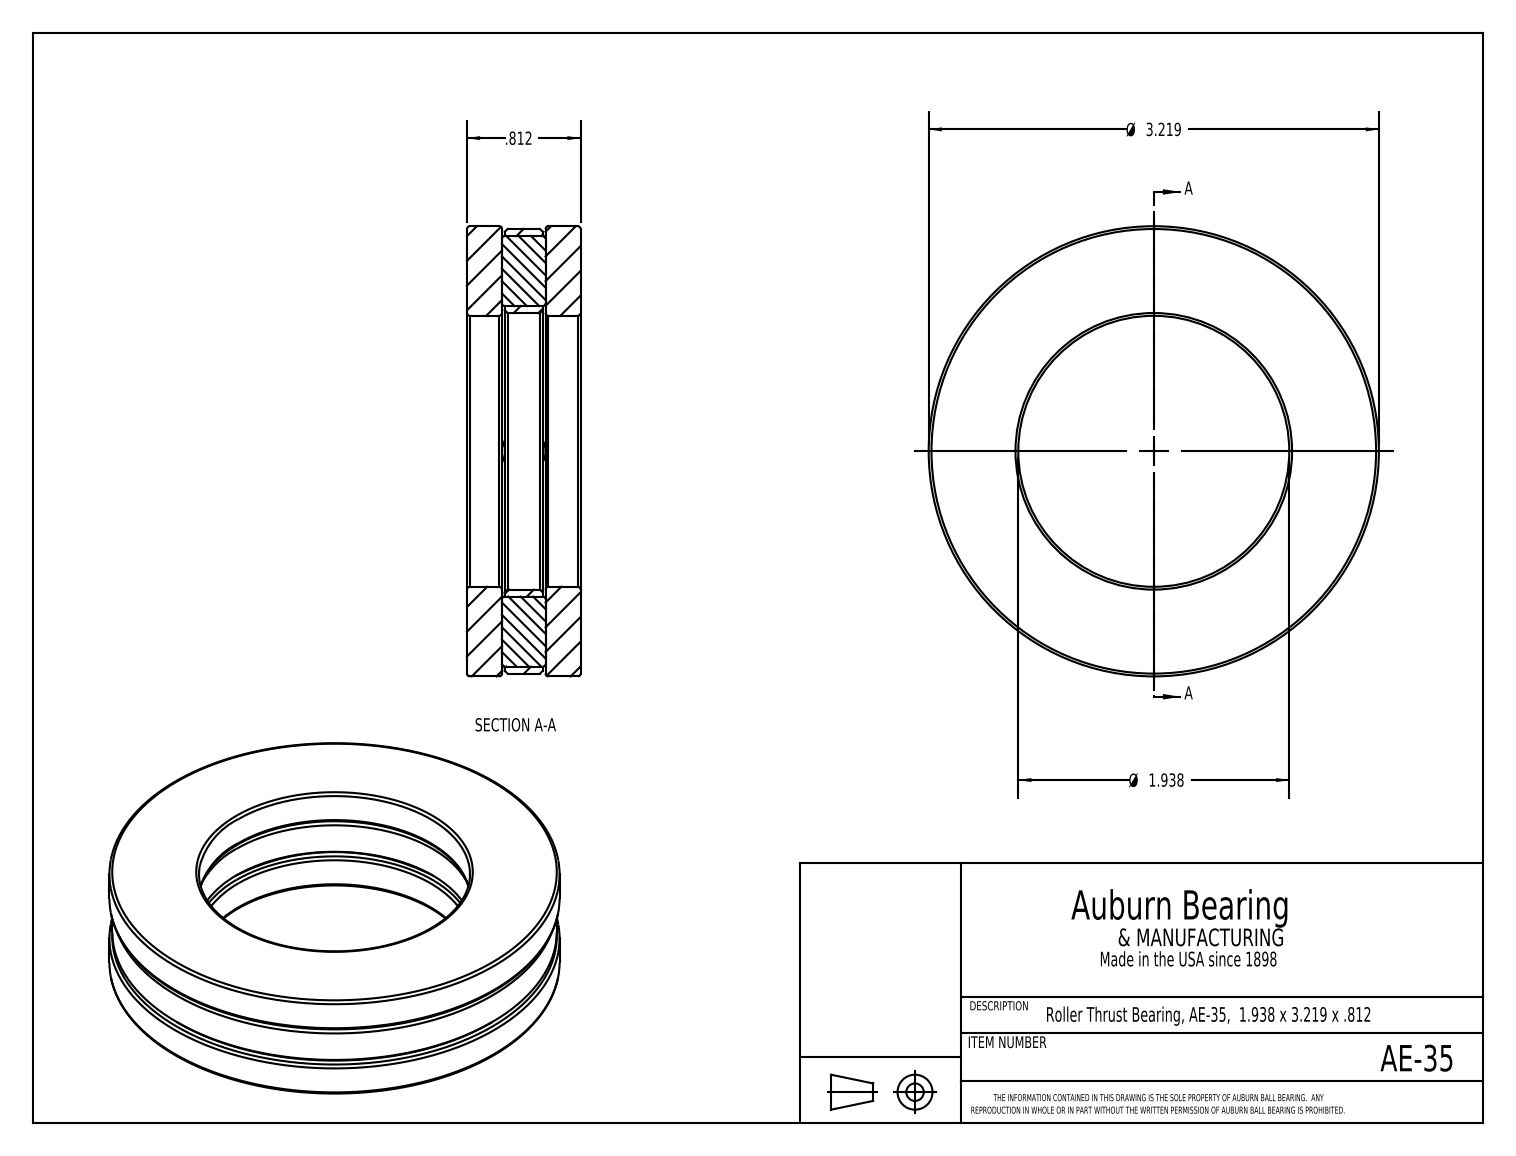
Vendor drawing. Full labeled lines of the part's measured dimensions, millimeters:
Part name (STEP PRODUCT): AE-35
STEP written by: SolidWorks 2017 (CONFIG_CONTROL_DESIGN)
Units: millimetres
Bodies: 7 solids, 60 faces (30 planar, 10 cylindrical, 20 other)
Overall size (bounding box): 81.8 × 81.8 × 20.6
Volume: 63 710 mm³ · Surface area: 29 080 mm²
Round holes (diameter × count): ⌀49.2 ×1, ⌀50.2 ×1
Round bosses / shafts (diameter × count): ⌀7.9 ×2, ⌀81.8 ×1, ⌀80.7 ×1
Main face-to-face distances: 6.4, 14.3, 6.9, 13.8, 0.5, 7.4, 7.9, 20.6, 6.9, 22.4
